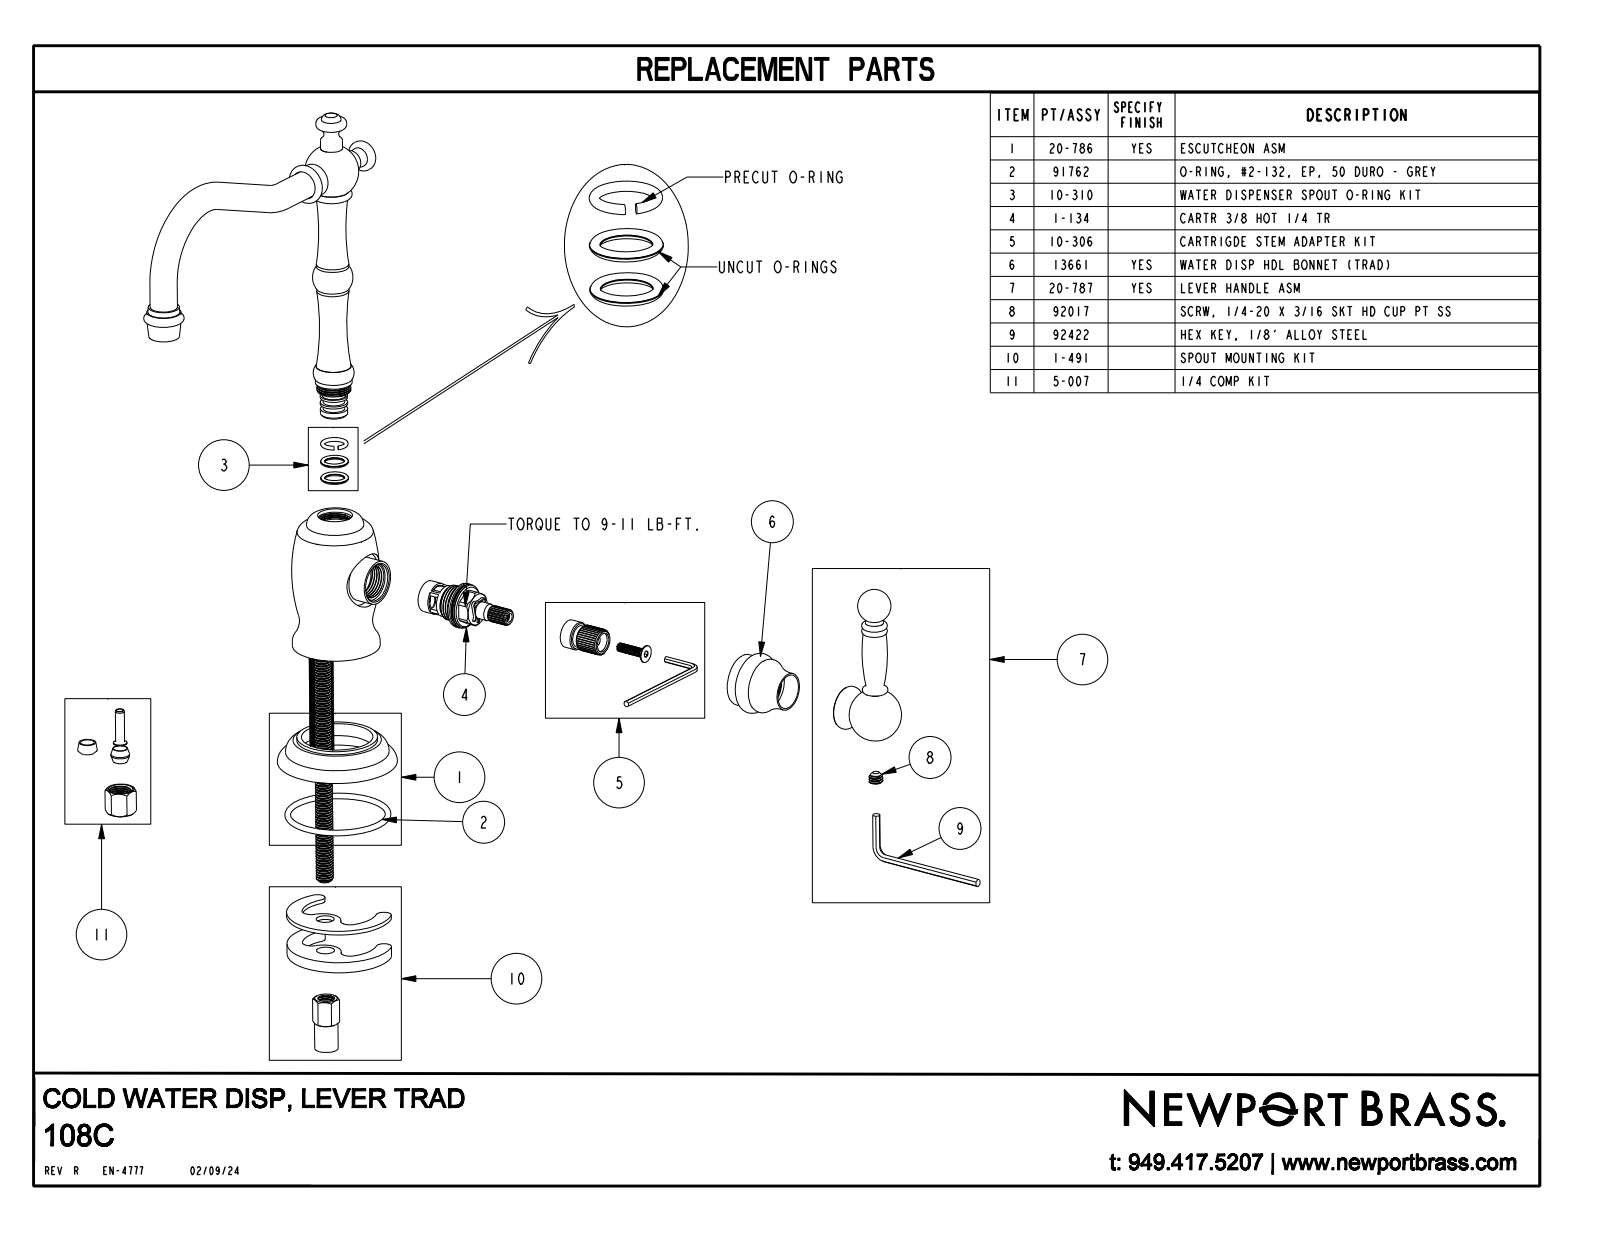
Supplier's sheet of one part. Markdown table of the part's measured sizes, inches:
| quantity | value |
| --- | --- |
| part name | 108C |
| STEP written by | CREO PARAMETRIC BY PTC INC, 2018400 (CONFIG_CONTROL_DESIGN) |
| units | inches |
| bodies | 1 solid, 155 faces (19 planar, 38 cylindrical, 98 other) |
| overall size | 8.195 × 6.653 × 3.818 |
| volume | 9.922 in³ |
| surface area | 51.6 in² |
| round holes (diameter × count) | 1 × 1 |
| round bosses / shafts (diameter × count) | 0.5 × 3, 0.6 × 2, 0.562 × 2, 0.405 × 2, 0.357 × 2, 1.61 × 1, 0.95 × 1, 0.675 × 1 |
| main face-to-face distances | 5.768, 0.02, 0.156, 0.243, 0.087, 1.02, 1, 6.343, 0.575, 7.952 |
